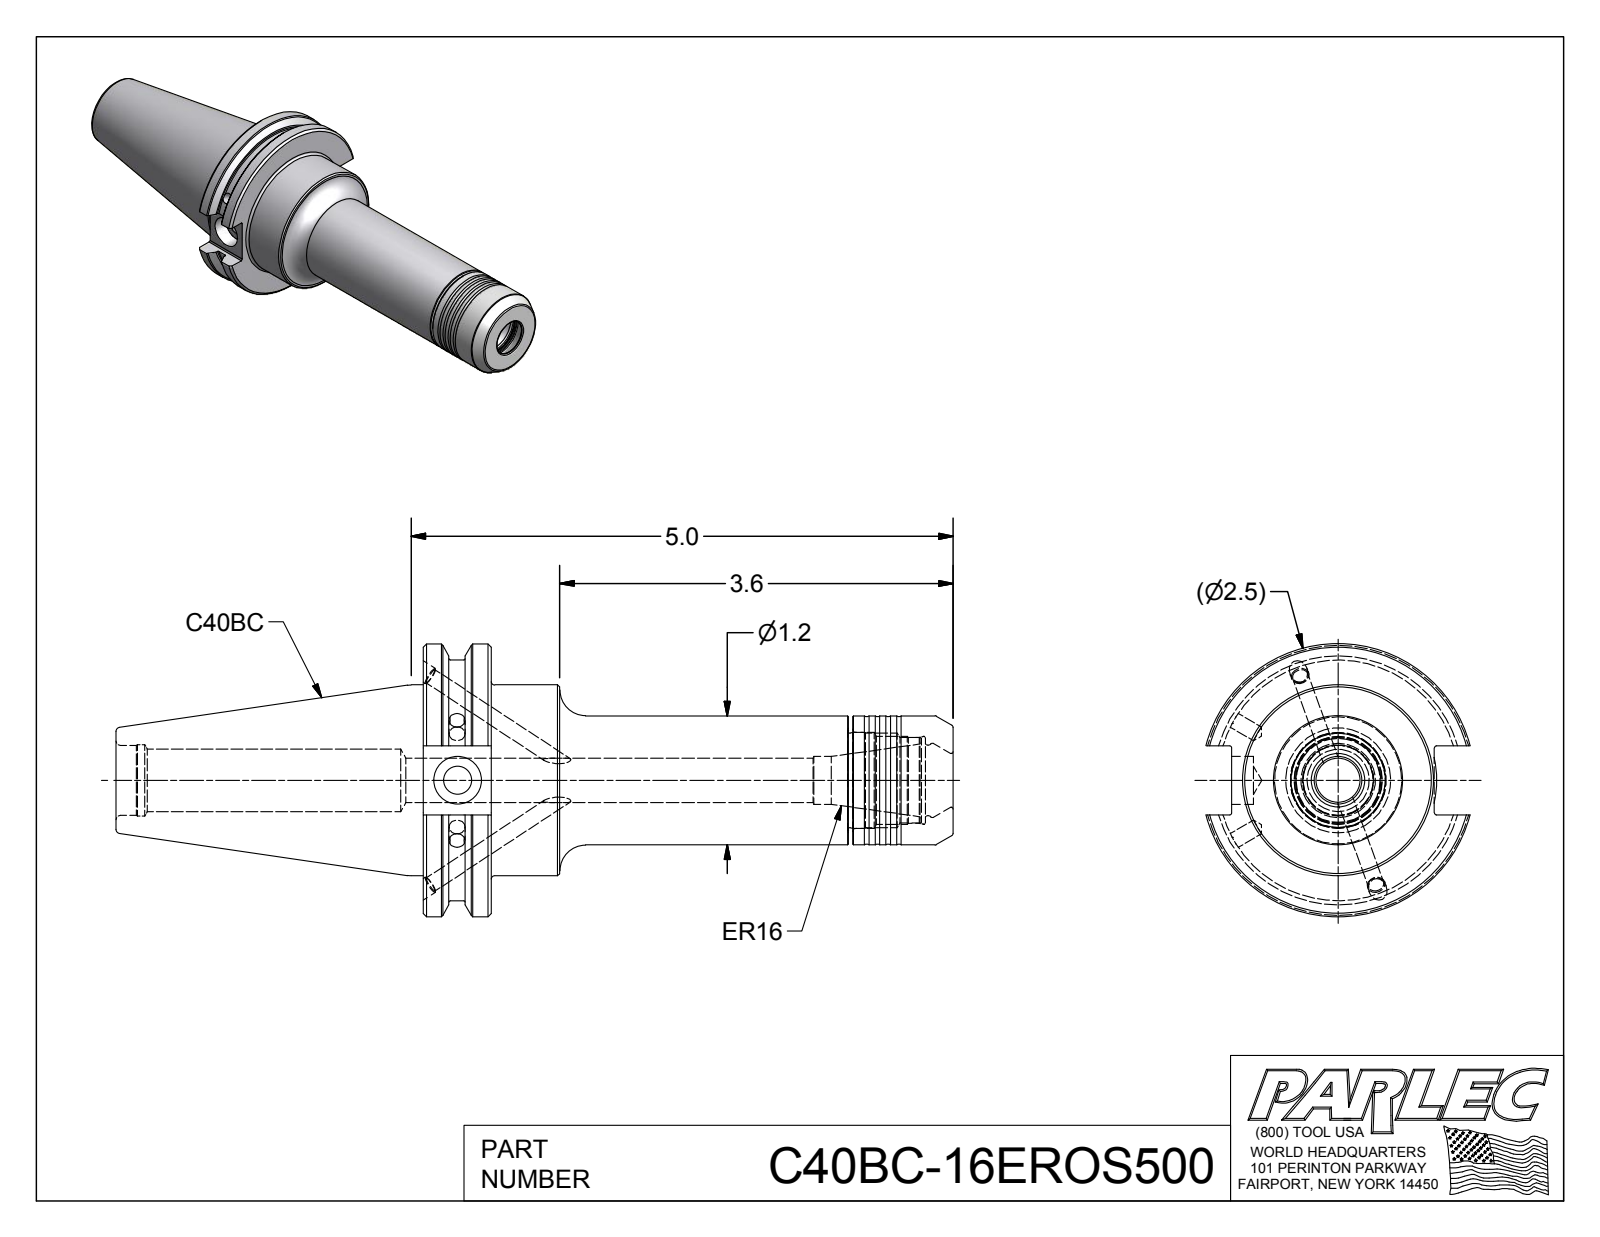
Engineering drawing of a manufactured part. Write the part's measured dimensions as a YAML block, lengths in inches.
part_name: "C40BC-16EROS500; 4481200_ohne Beschriftung; 44375951270"
step_written_by: "Autodesk Inventor 2012 (AUTOMOTIVE_DESIGN)"
units: inches
bodies: {solids: 2, faces: 128, planar: 25, cylindrical: 41, other: 62}
overall_size: [7.672, 2.502, 2.42]
volume: 10.83
surface_area: 59.77
round_holes:
  - {diameter: 0.146, count: 4}
  - {diameter: 0.165, count: 2}
  - {diameter: 0.437, count: 2}
  - {diameter: 0.406, count: 1}
  - {diameter: 0.492, count: 1}
  - {diameter: 0.571, count: 1}
  - {diameter: 0.642, count: 1}
  - {diameter: 0.646, count: 1}
  - {diameter: 0.654, count: 1}
  - {diameter: 0.784, count: 1}
  - {diameter: 0.804, count: 1}
  - {diameter: 0.807, count: 1}
round_bosses_or_shafts:
  - {diameter: 2.502, count: 1}
  - {diameter: 1.75, count: 1}
  - {diameter: 1.181, count: 1}
  - {diameter: 0.878, count: 1}
  - {diameter: 0.866, count: 1}
  - {diameter: 0.783, count: 1}
partial_cylinders:
  - {radius: 0.02, count: 4}
  - {radius: 1.102, count: 1}
face_to_face_distances: [0.626, 4.857, 4.231, 0.039, 3.936, 3.31, 0.921, 3.898, 3.272, 0.96]
